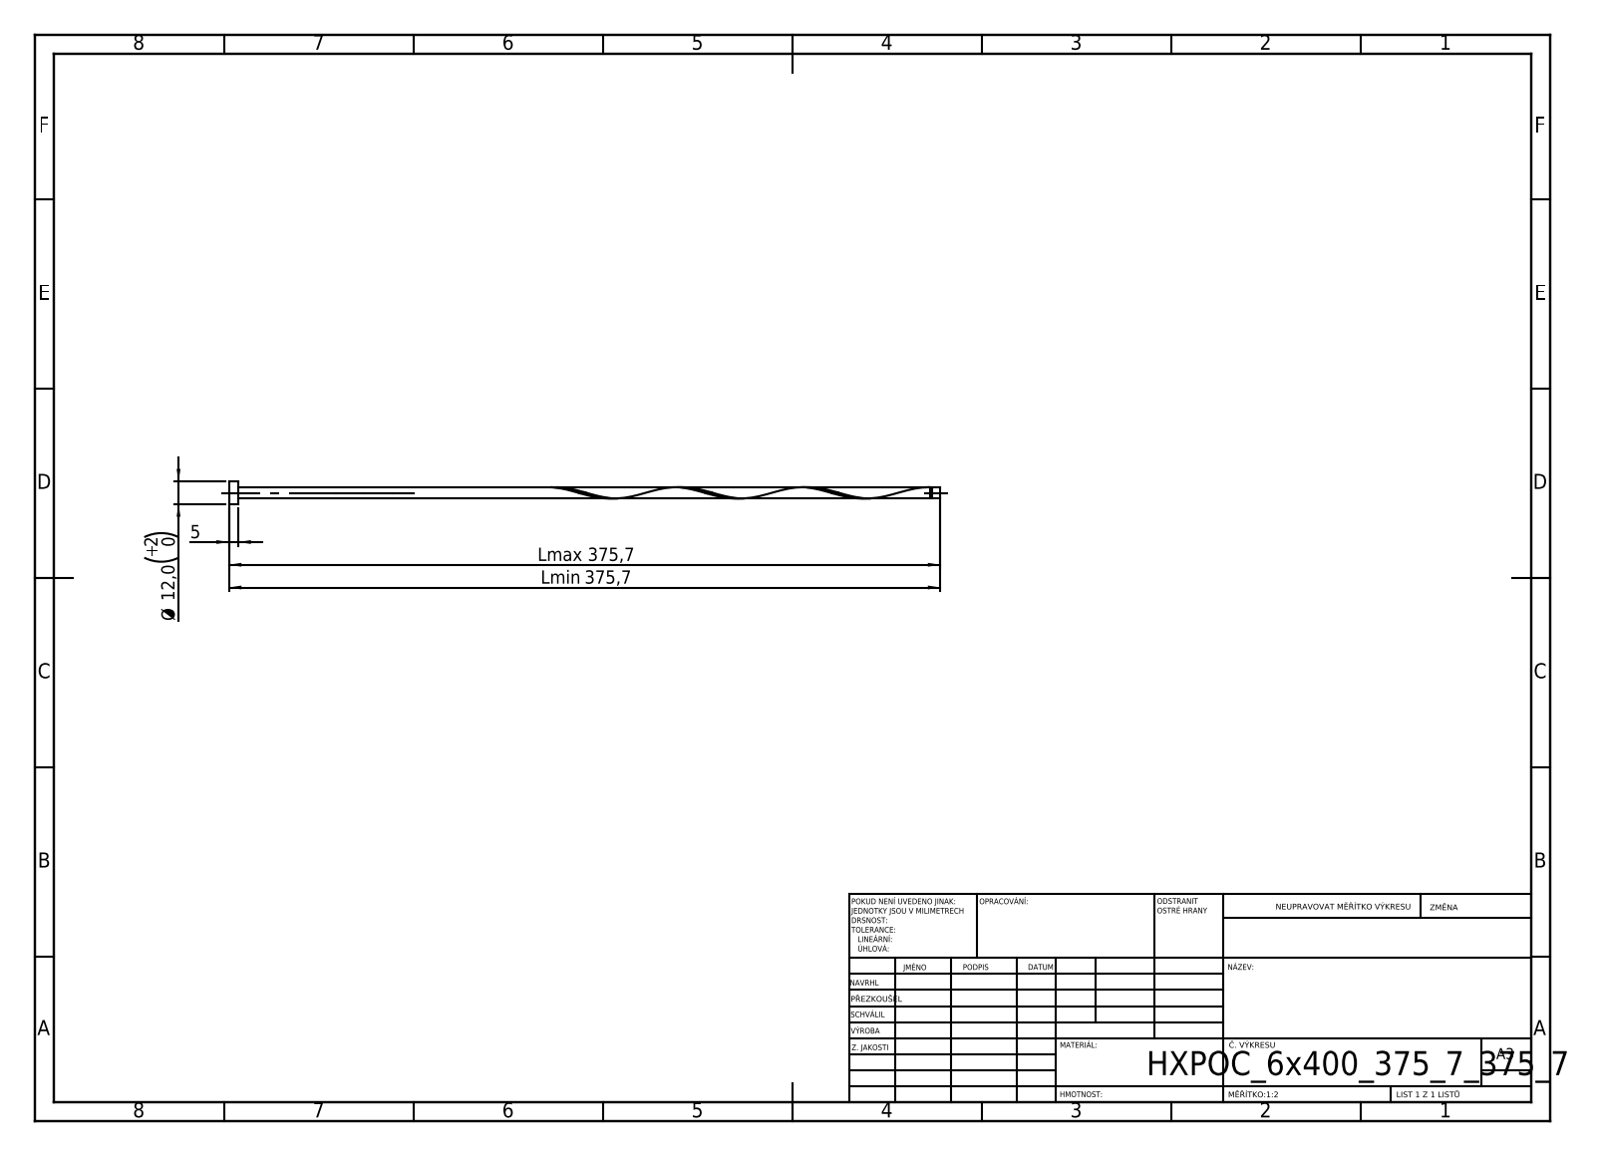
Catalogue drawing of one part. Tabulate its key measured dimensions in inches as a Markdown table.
| quantity | value |
| --- | --- |
| STEP written by | SolidWorks 2019 (CONFIG_CONTROL_DESIGN) |
| units | inches |
| bodies | 1 solid, 16 faces (6 planar, 9 cylindrical, 1 other) |
| overall size | 14.791 × 0.472 × 0.472 |
| volume | 0.82 in³ |
| surface area | 15.58 in² |
| round bosses / shafts (diameter × count) | 0.472 × 1, 0.236 × 1, 0.189 × 1 |
| main face-to-face distances | 0.197, 14.791, 14.594, 14.615, 14.418, 0.176, 14.568, 14.371, 0.047, 0.224 |
